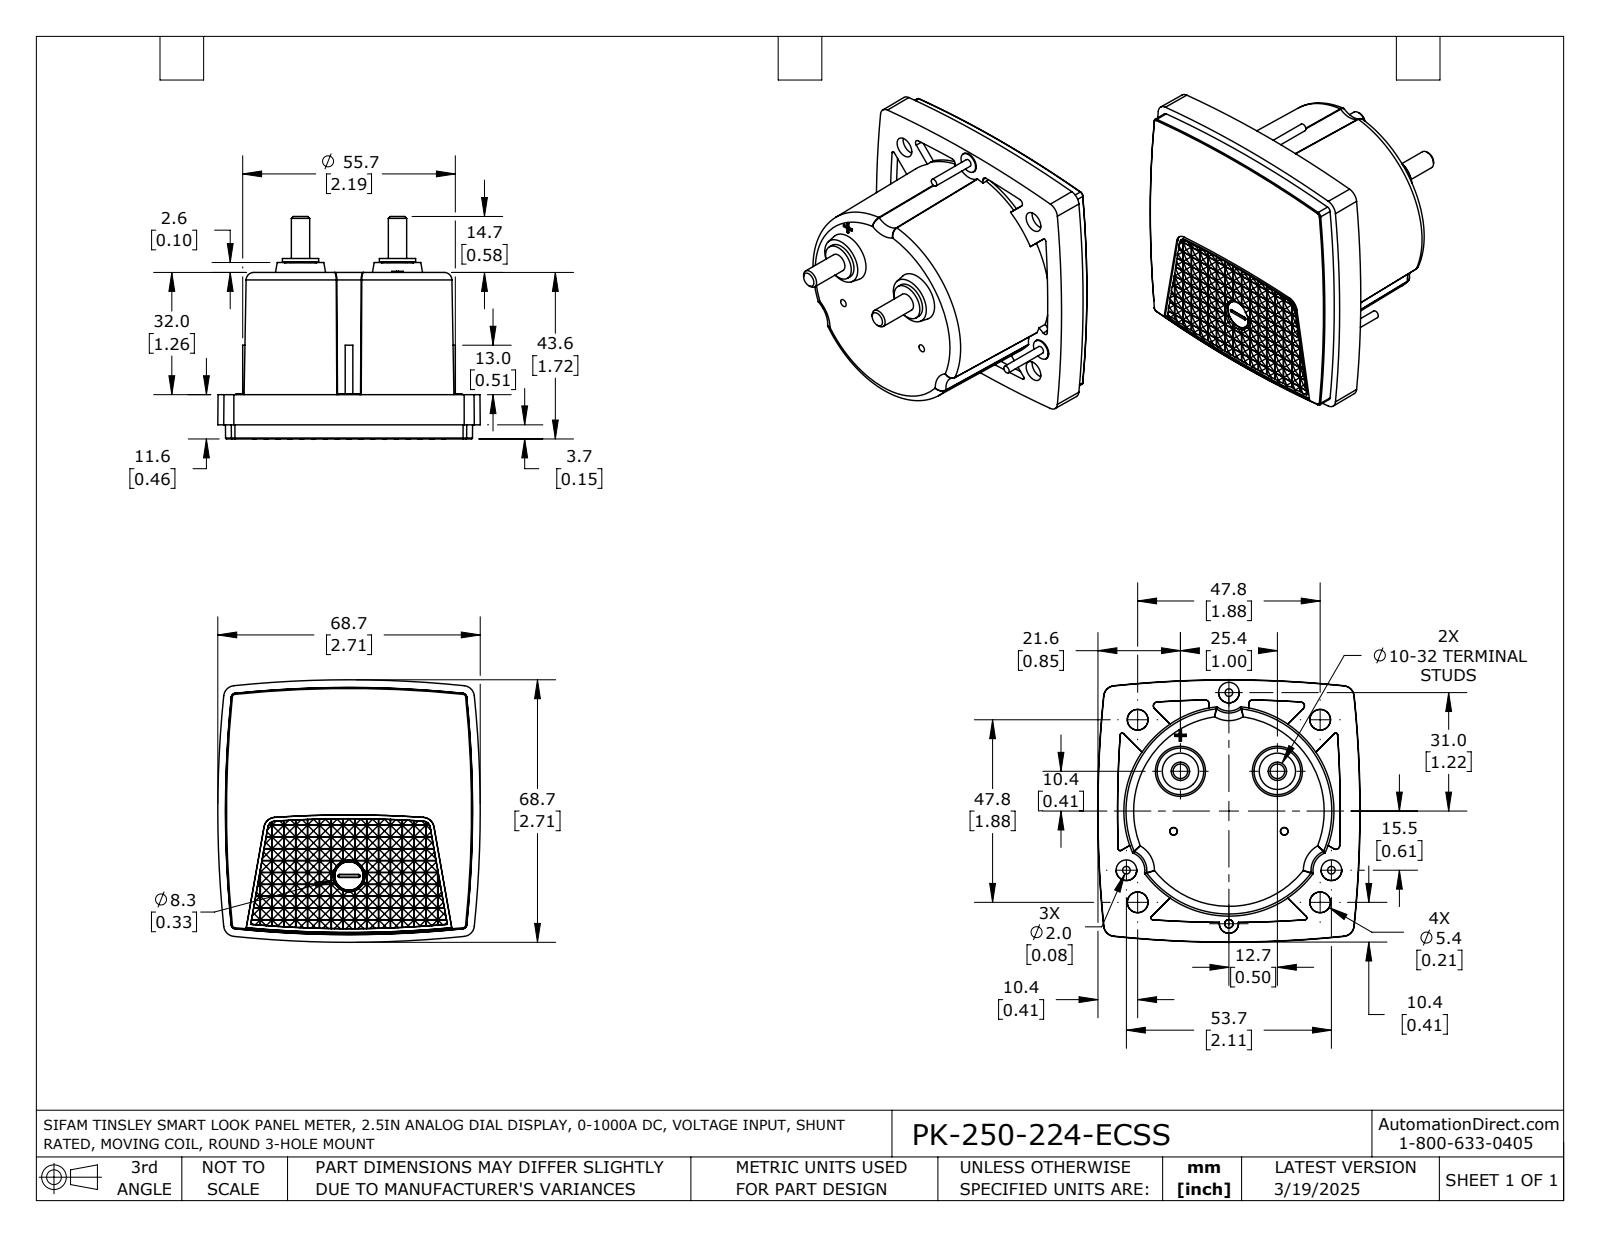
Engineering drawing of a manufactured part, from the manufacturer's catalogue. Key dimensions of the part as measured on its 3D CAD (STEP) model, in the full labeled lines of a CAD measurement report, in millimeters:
Part name (STEP PRODUCT): PK-250-224-ECSS
STEP written by: SolidWorks 2021 (AUTOMOTIVE_DESIGN)
Units: millimetres
Bodies: 1 solid, 1550 faces (1165 planar, 265 cylindrical, 120 other)
Overall size (bounding box): 68.7 × 68.7 × 58.3
Volume: 124 400 mm³ · Surface area: 19 620 mm²
Round bosses / shafts (diameter × count): ⌀5.4 ×3, ⌀2 ×3, ⌀9.5 ×2, ⌀4.8 ×2, ⌀5.5 ×1
Partial cylindrical surfaces — rounded edges, fillets, slot ends (radius × count): R4.2 ×2, R27.5 ×1
Main face-to-face distances: 43.6, 32, 11.6, 0.6, 2.2, 2.4, 7.9, 3, 1.8, 34.2
